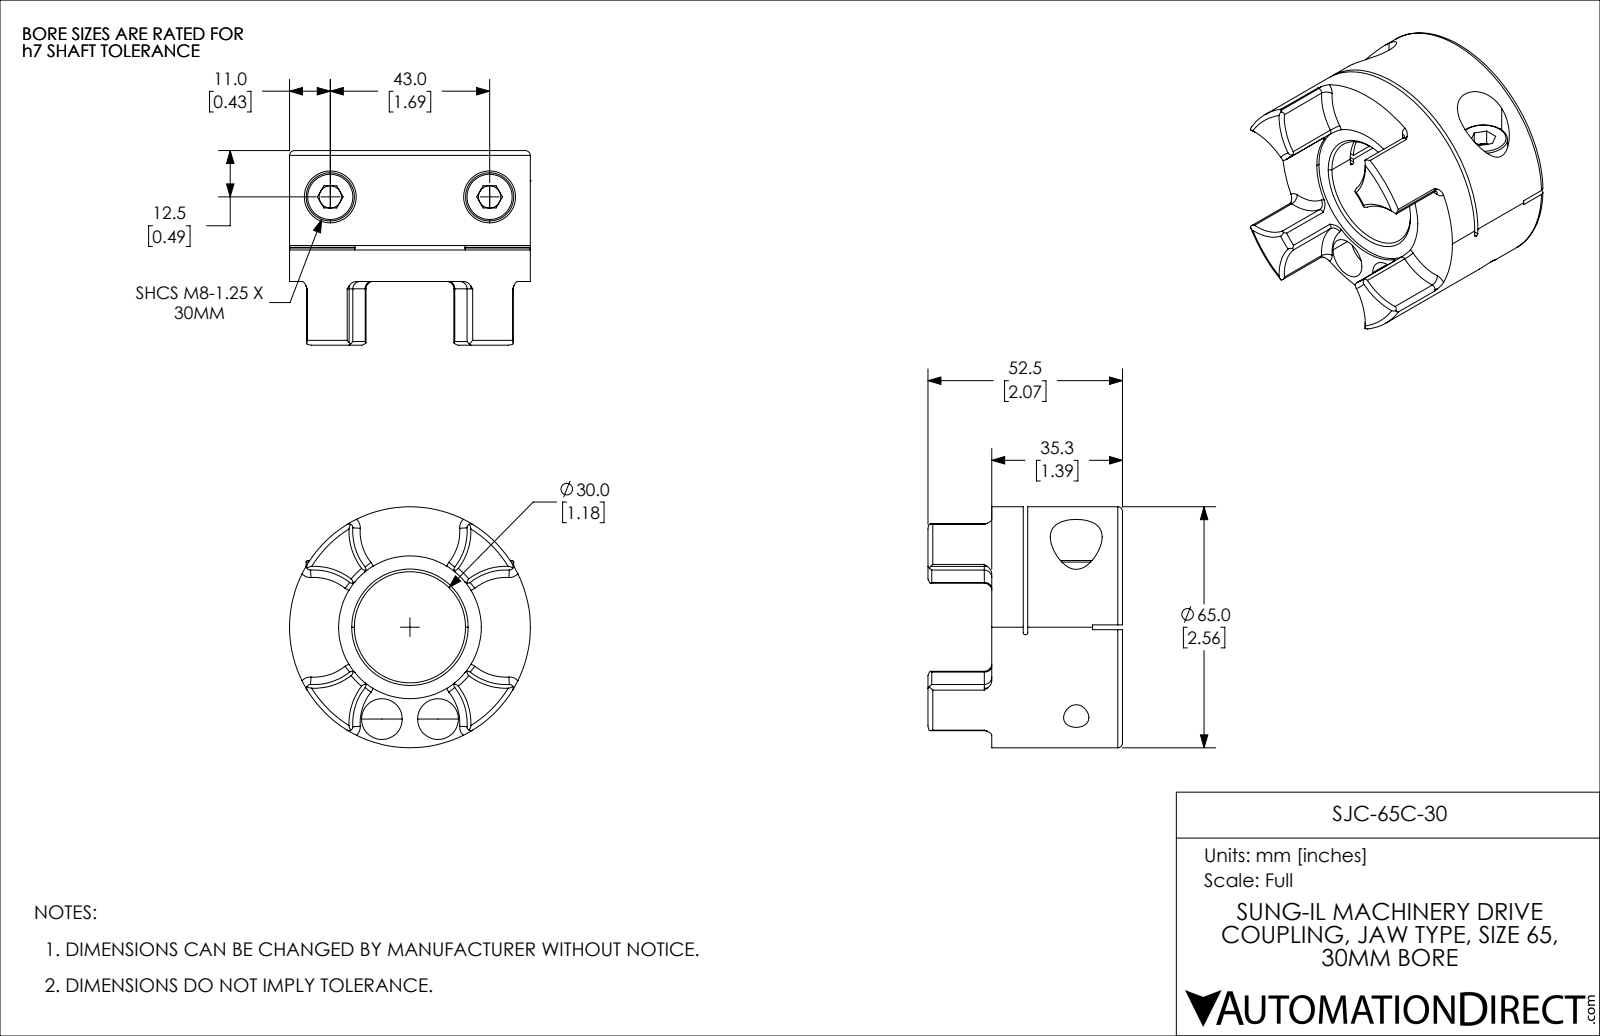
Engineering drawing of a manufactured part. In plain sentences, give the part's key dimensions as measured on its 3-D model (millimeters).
The part is named "SJC-65C-30". Its 3-D file was written by "SolidWorks 2021 (CONFIG_CONTROL_DESIGN)". It is 3 solids with 207 faces: 52 planar, 73 cylindrical and 82 other. Overall it measures 65 by 65 by 52.5 millimeters. Its volume is 94 611 cubic millimeters and its surface area 28 197 square millimeters. Round holes: 2 of diameter 6, 2 of diameter 6.8, 2 of diameter 8.5, 2 of diameter 11, 2 of diameter 14, 1 of diameter 30, 1 of diameter 38.5. Round bosses or shafts: 2 of diameter 13, 2 of diameter 8, 1 of diameter 65. Partial cylindrical surfaces (rounded edges, fillets, slot ends): 16 of radius 1, 4 of radius 15.45, 2 of radius 0.5, 1 of radius 50. The main face-to-face distances are 26.8, 1.2, 25.6, 8.5, 9.7, 35.3, 1.3, 0.8, 7.7, 8.9. The hole center spacings are 25.89, 15.14, 43.
